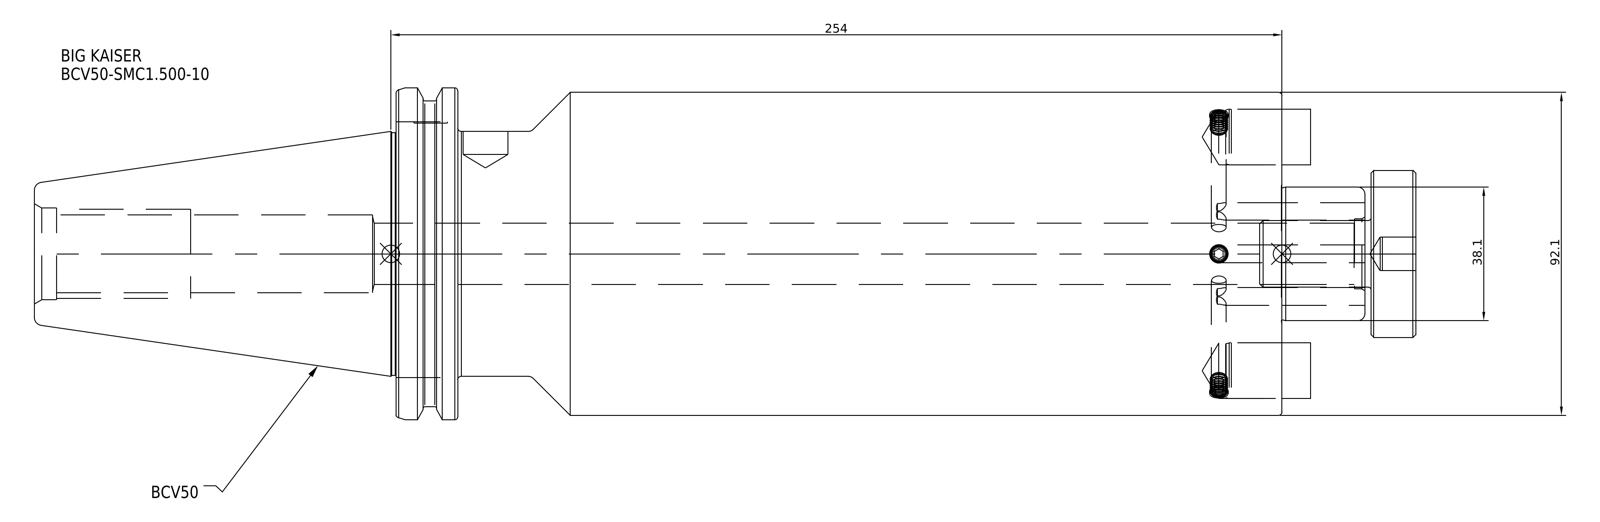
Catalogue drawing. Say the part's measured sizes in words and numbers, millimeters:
The part is named "BCV50-SMC1_500-10". Its 3-D file was written by "SolidWorks 2021 (CONFIG_CONTROL_DESIGN)". It is 1 solid with 39 faces: 17 planar, 14 cylindrical and 8 other. Overall it measures 363.68 by 98.43 by 98.43 millimeters. Its volume is 1 822 000 cubic millimeters and its surface area 120 642 square millimeters. Round holes: 1 of diameter 17.46. Round bosses or shafts: 1 of diameter 98.43, 1 of diameter 92.1, 1 of diameter 91.29, 1 of diameter 69.85. The main face-to-face distances are 252.5, 234.95, 17.55, 355.6, 120.65, 103.1, 15.88, 8.08, 243.03, 260.58.
